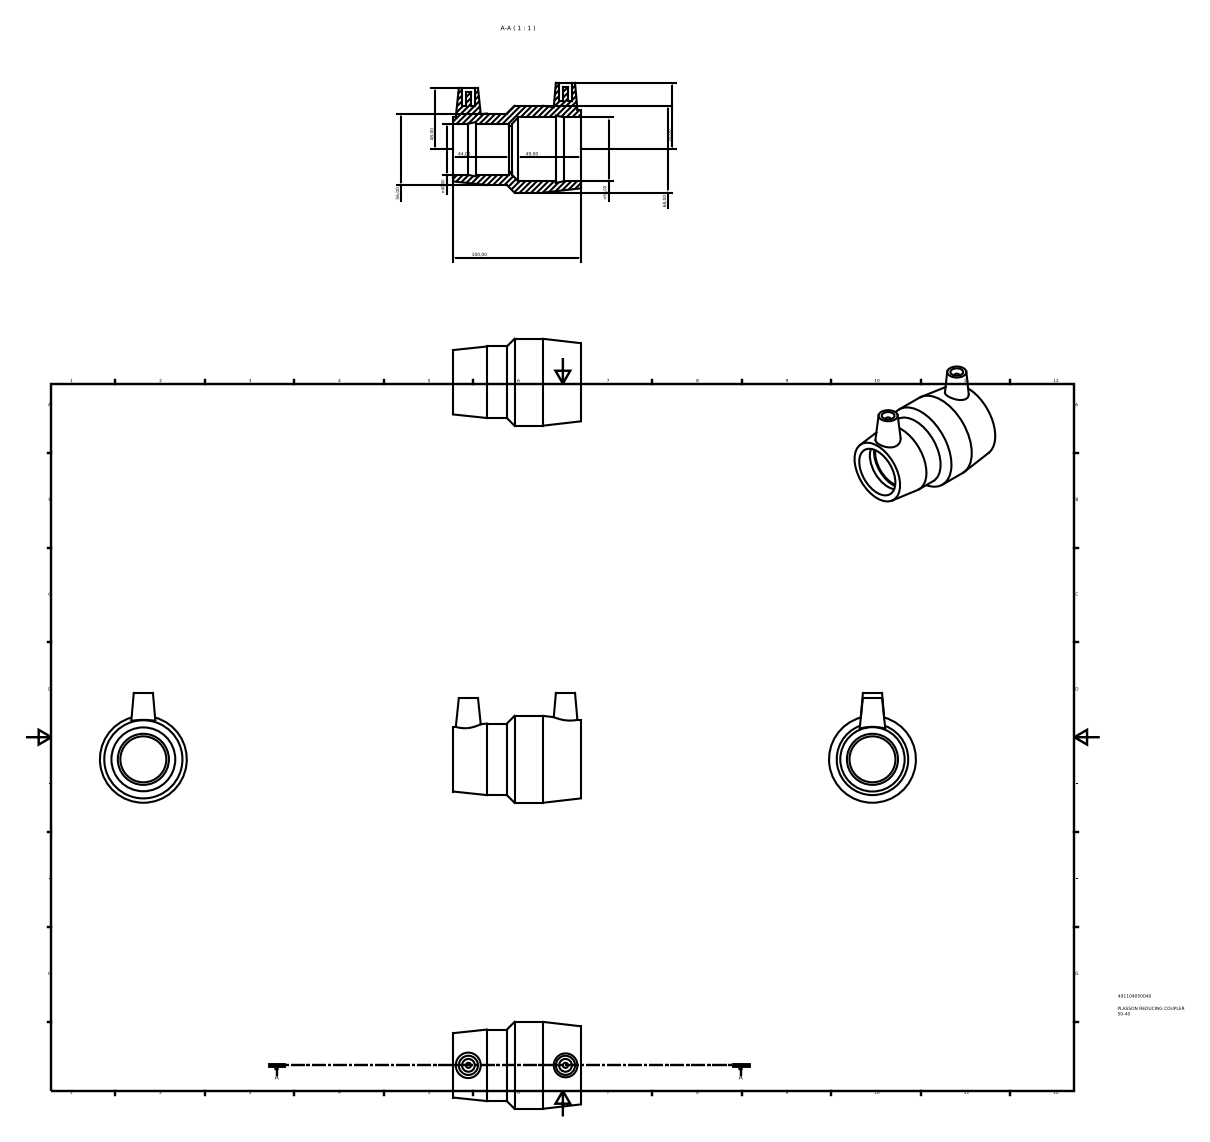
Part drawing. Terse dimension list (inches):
name: 491104050040
written by: Autodesk Inventor 2015 (AUTOMOTIVE_DESIGN)
unit: in
bodies: 1 solid, 31 faces (12 planar, 11 cylindrical, 8 other)
size: 3.937 × 3.386 × 2.677
volume: 8.479 in³; area: 62.07 in²
holes: 2× ⌀0.394, 1× ⌀1.417, 1× ⌀1.575, 1× ⌀1.969
bosses: 2× ⌀0.157, 1× ⌀2.677, 1× ⌀2.205
face distances: 3.937, 1.819, 2.118, 1.732, 0.087, 2.205, 3.165, 1.433, 1.346, 0.772
hole spacings: 2.992
